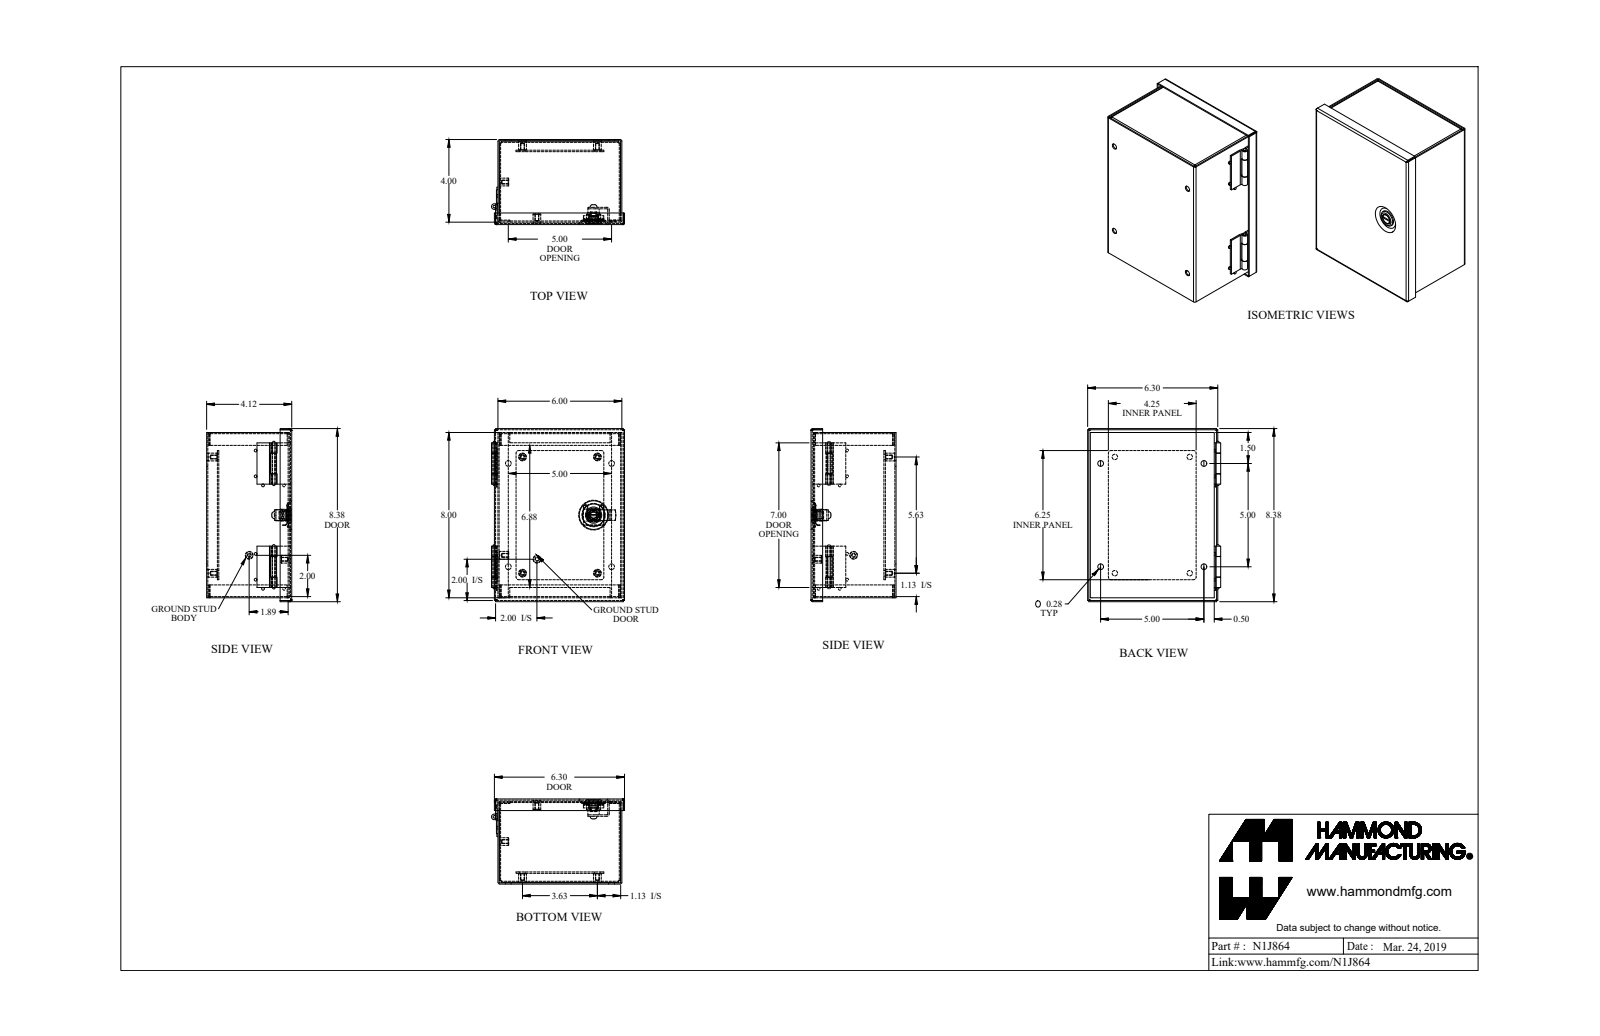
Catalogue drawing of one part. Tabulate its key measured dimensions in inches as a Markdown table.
| quantity | value |
| --- | --- |
| part name | N1J864 |
| STEP written by | SolidWorks 2018 (AUTOMOTIVE_DESIGN) |
| units | inches |
| bodies | 18 solids, 477 faces (224 planar, 188 cylindrical, 65 other) |
| overall size | 8.38 × 6.443 × 4.118 |
| volume | 17.23 in³ |
| surface area | 590.2 in² |
| round holes (diameter × count) | 0.156 × 6, 0.265 × 4, 0.28 × 4, 0.125 × 1, 0.319 × 1, 0.476 × 1 |
| round bosses / shafts (diameter × count) | 0.131 × 8, 0.375 × 5, 0.787 × 1, 0.547 × 1, 0.472 × 1, 0.469 × 1, 0.375 × 1, 0.366 × 1 |
| partial cylindrical surfaces (radius × count) | 0.029 × 16, 0.086 × 16, 0.012 × 4, 0.1 × 4, 0.125 × 4, 0.036 × 2, 0.079 × 2, 0.25 × 2 |
| main face-to-face distances | 0.057, 4.061, 5.943, 4.004, 4.118, 7.943, 6, 5.886, 0.072, 0.517 |
| hole center spacings | 0.755, 4.324, 5, 5.357, 6.843, 2.648, 2.819, 3.625 |
